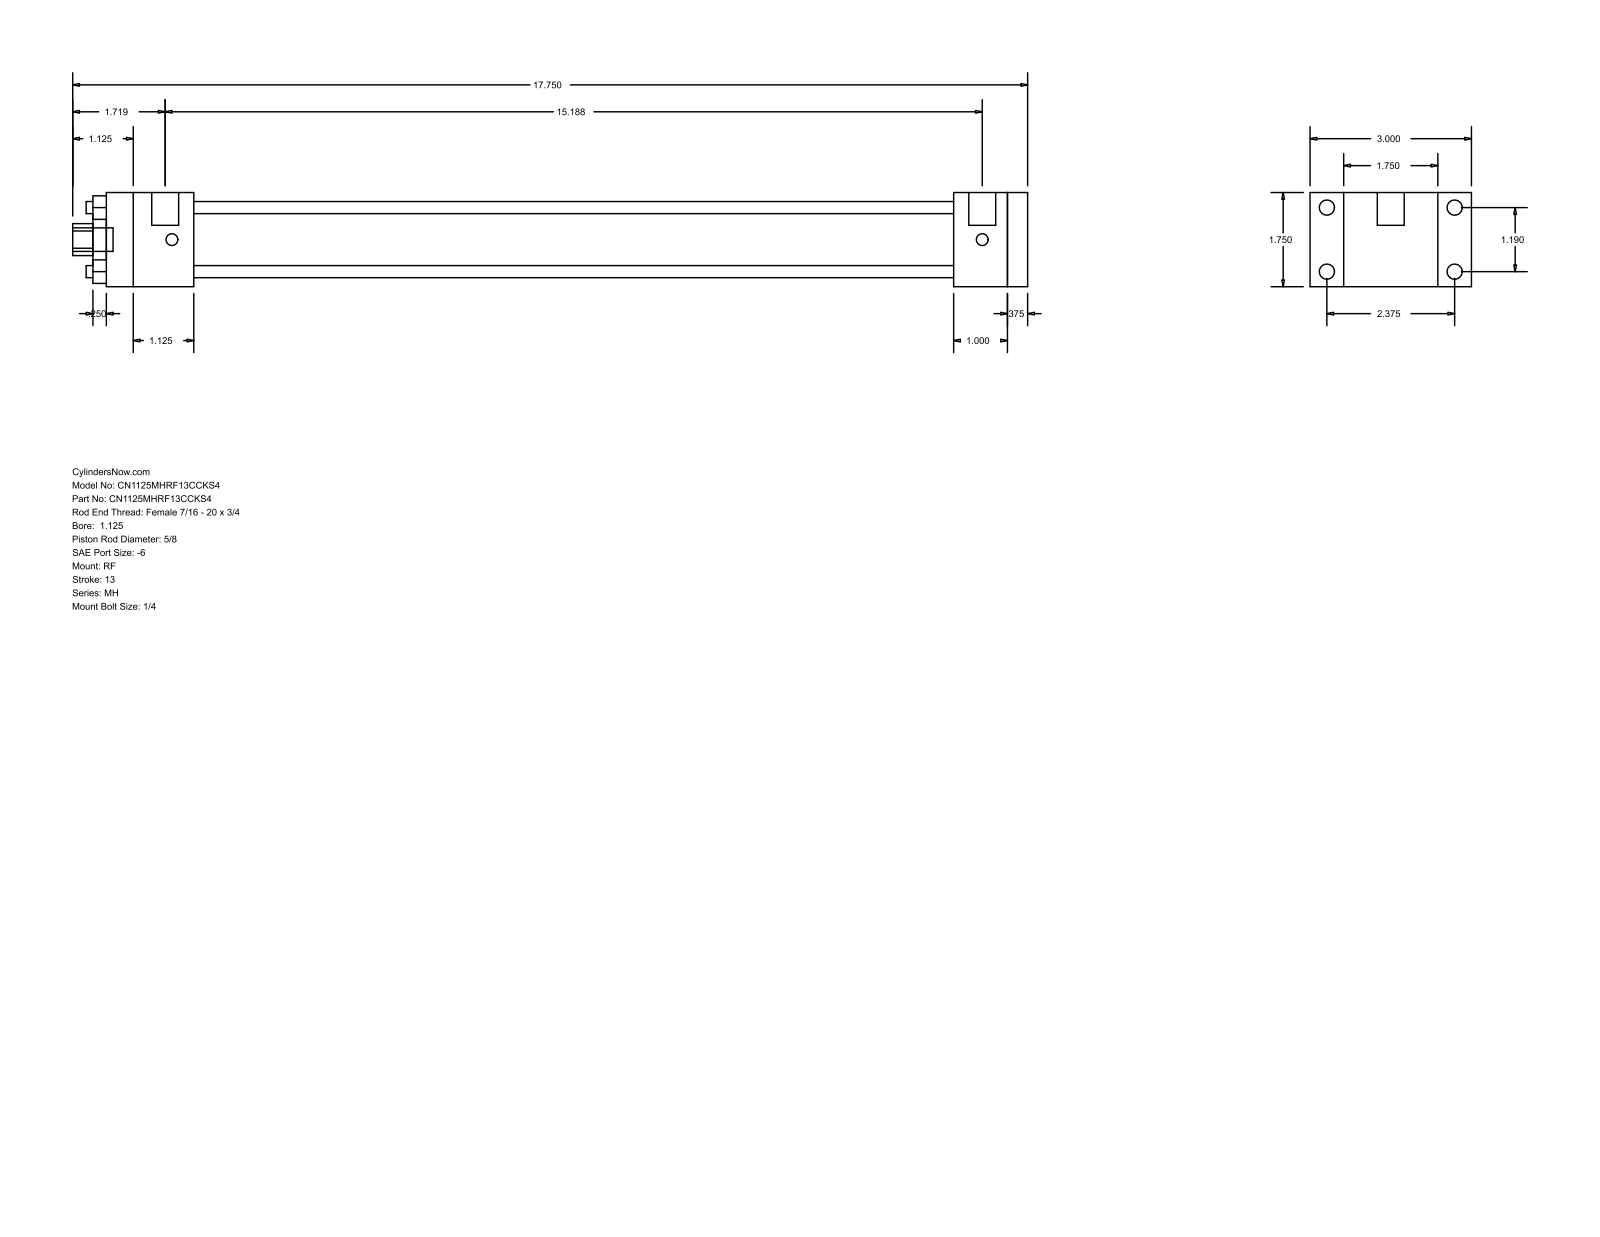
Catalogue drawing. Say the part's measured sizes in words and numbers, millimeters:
The part is named "MH_RF__0112_0.625". Its 3-D file was written by "GSSL Pune (CONFIG_CONTROL_DESIGN)". It is 0 solids with 92 faces: 64 planar, 28 cylindrical and 0 other. Overall it measures 450.85 by 76.2 by 44.45 millimeters. Round holes: 4 of diameter 5.71, 1 of diameter 15.88, 1 of diameter 28.57, 1 of diameter 34.92. Round bosses or shafts: 4 of diameter 7.14, 4 of diameter 5.56, 2 of diameter 12.7, 1 of diameter 11.11. Partial cylindrical surfaces (rounded edges, fillets, slot ends): 1 of radius 7.54. The main face-to-face distances are 44.46, 9.53, 434.97, 15.87, 384.17, 393.7, 358.78, 25.39, 34.92, 41.27. The hole center spacings are 21.37, 30.22, 42.74.
